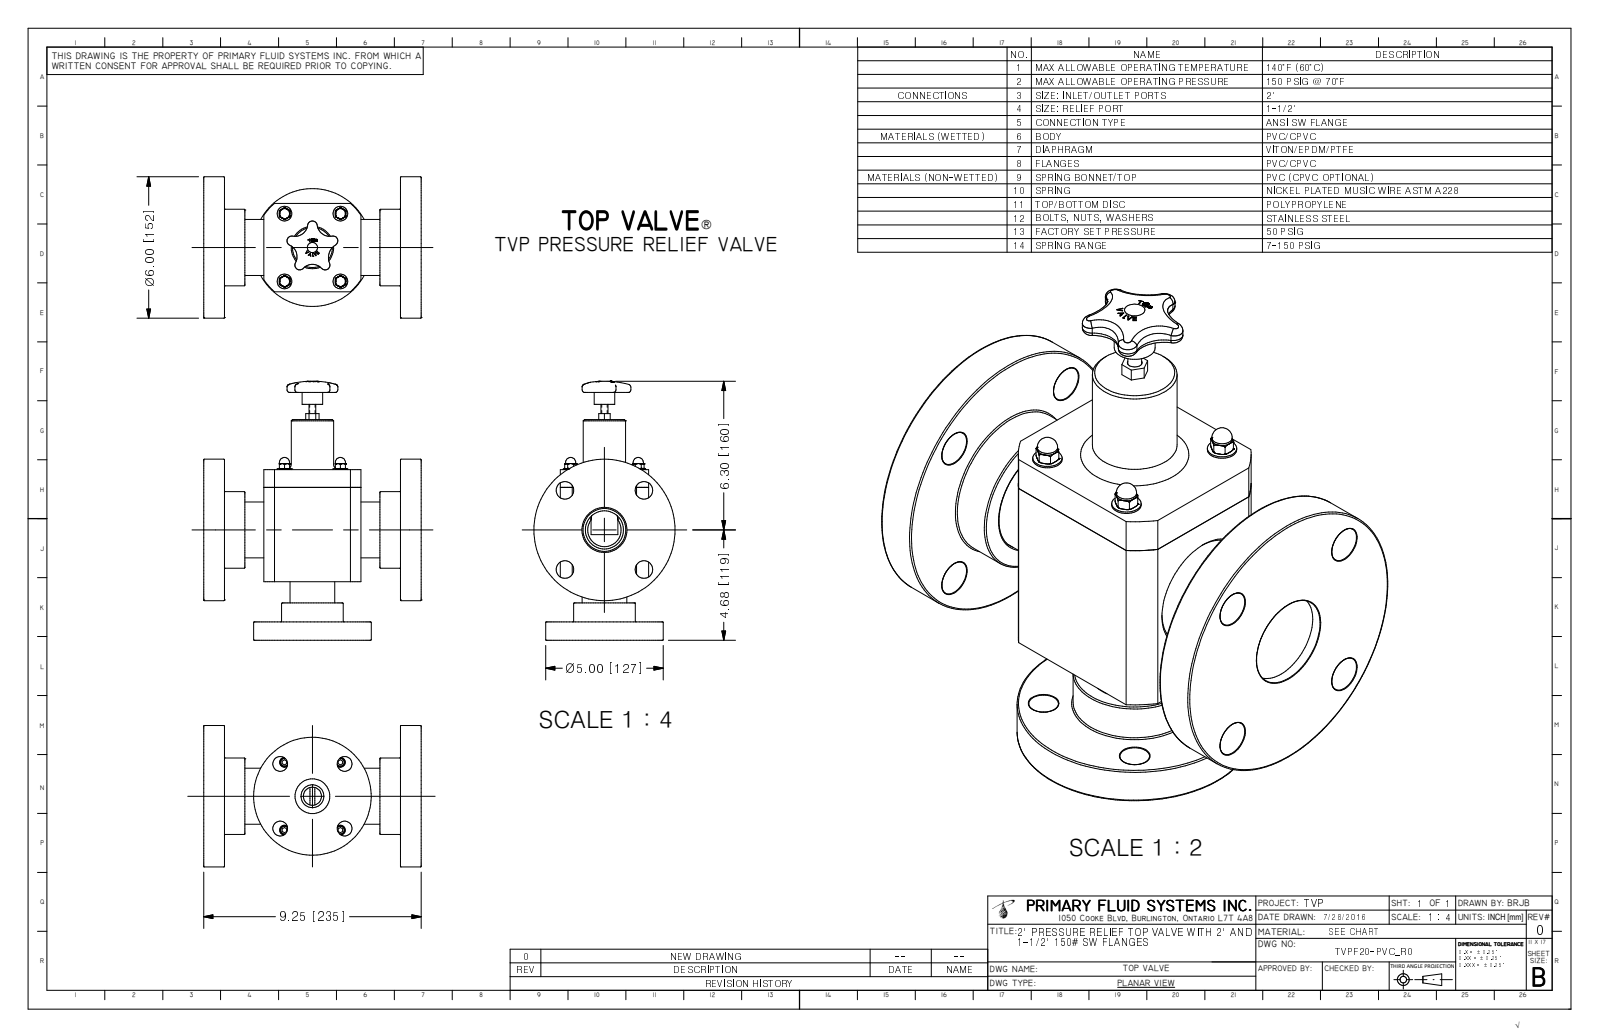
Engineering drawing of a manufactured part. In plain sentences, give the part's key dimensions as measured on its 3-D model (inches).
The part is named "TVPF20-PVC_R0". Its 3-D file was written by "Autodesk Inventor 2009 (AUTOMOTIVE_DESIGN)". It is 1 solid with 441 faces: 162 planar, 79 cylindrical and 200 other. Overall it measures 10.982 by 9.25 by 6 inches. Its volume is 140.7 cubic inches and its surface area 482.7 square inches. Round holes: 4 of diameter 0.175, 4 of diameter 0.63, 4 of diameter 0.745, 1 of diameter 0.77, 1 of diameter 1.476, 1 of diameter 1.5, 1 of diameter 1.856, 1 of diameter 1.913, 1 of diameter 1.939. Round bosses or shafts: 4 of diameter 0.625, 4 of diameter 0.433, 4 of diameter 0.375, 1 of diameter 6, 1 of diameter 5, 1 of diameter 3.244, 1 of diameter 2.62, 1 of diameter 2.375. Partial cylindrical surfaces (rounded edges, fillets, slot ends): 5 of radius 0.085, 5 of radius 0.205, 4 of radius 0.536, 4 of radius 0.656, 1 of radius 0.625, 1 of radius 0.745, 1 of radius 2.475. The main face-to-face distances are 0.885, 8.365, 9.25, 7.48, 2.563, 6.688, 1.678, 5.803, 3.75, 0.78. The hole center spacings are 1.937, 2.375, 2.558, 2.74, 3.359, 0.194, 0.195, 1.864.
